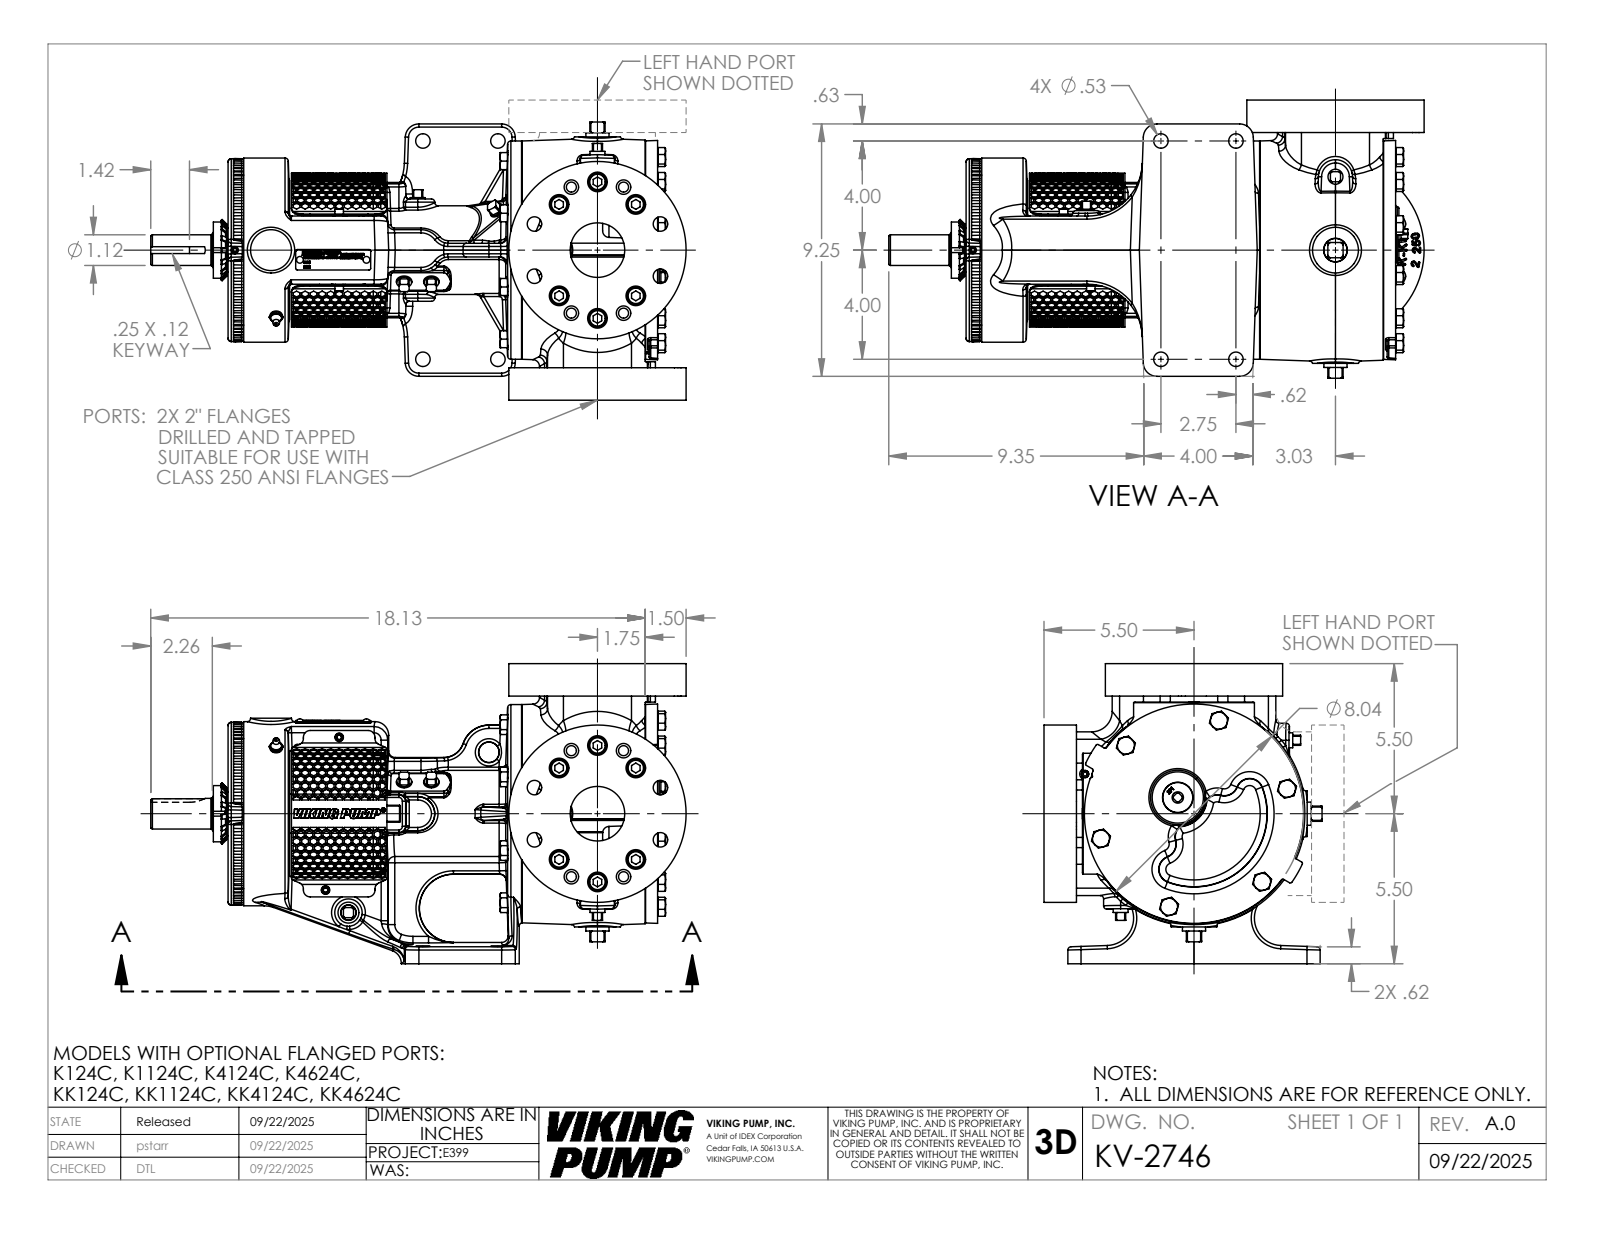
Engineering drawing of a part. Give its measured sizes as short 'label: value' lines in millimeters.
name: KV-2746
written by: SolidWorks 2024 (AUTOMOTIVE_DESIGN)
unit: mm
bodies: 1 solid, 4362 faces (1507 planar, 609 cylindrical, 2246 other)
size: 498.58 × 279.4 × 258.95
volume: 8 999 000 mm³; area: 684 924 mm²
holes: 16× ⌀13.49, 12× ⌀18.26, 9× ⌀6.35, 8× ⌀9.35, 8× ⌀19.81, 6× ⌀5.02, 4× ⌀13.49, 2× ⌀4.04, 2× ⌀7.94, 2× ⌀50.8, 1× ⌀6.53, 1× ⌀11.51
bosses: 23× ⌀15.88, 3× ⌀15.87, 3× ⌀7.92, 3× ⌀4.83, 2× ⌀165.1, 1× ⌀203.2, 1× ⌀171.45, 1× ⌀139.62
rounds: 77× R3.05, 18× R0.76, 18× R6.1, 18× R25.4, 16× R3.05, 10× R6.35, 10× R12.7, 8× R1.52
face distances: 279.4, 30.23, 400.03, 12.7, 135.23, 264.8, 14.58, 120.65, 385.45, 249.17
hole spacings: 63.5, 76.2, 26.16, 48.6, 24.78, 29.33, 34.96, 55.56
